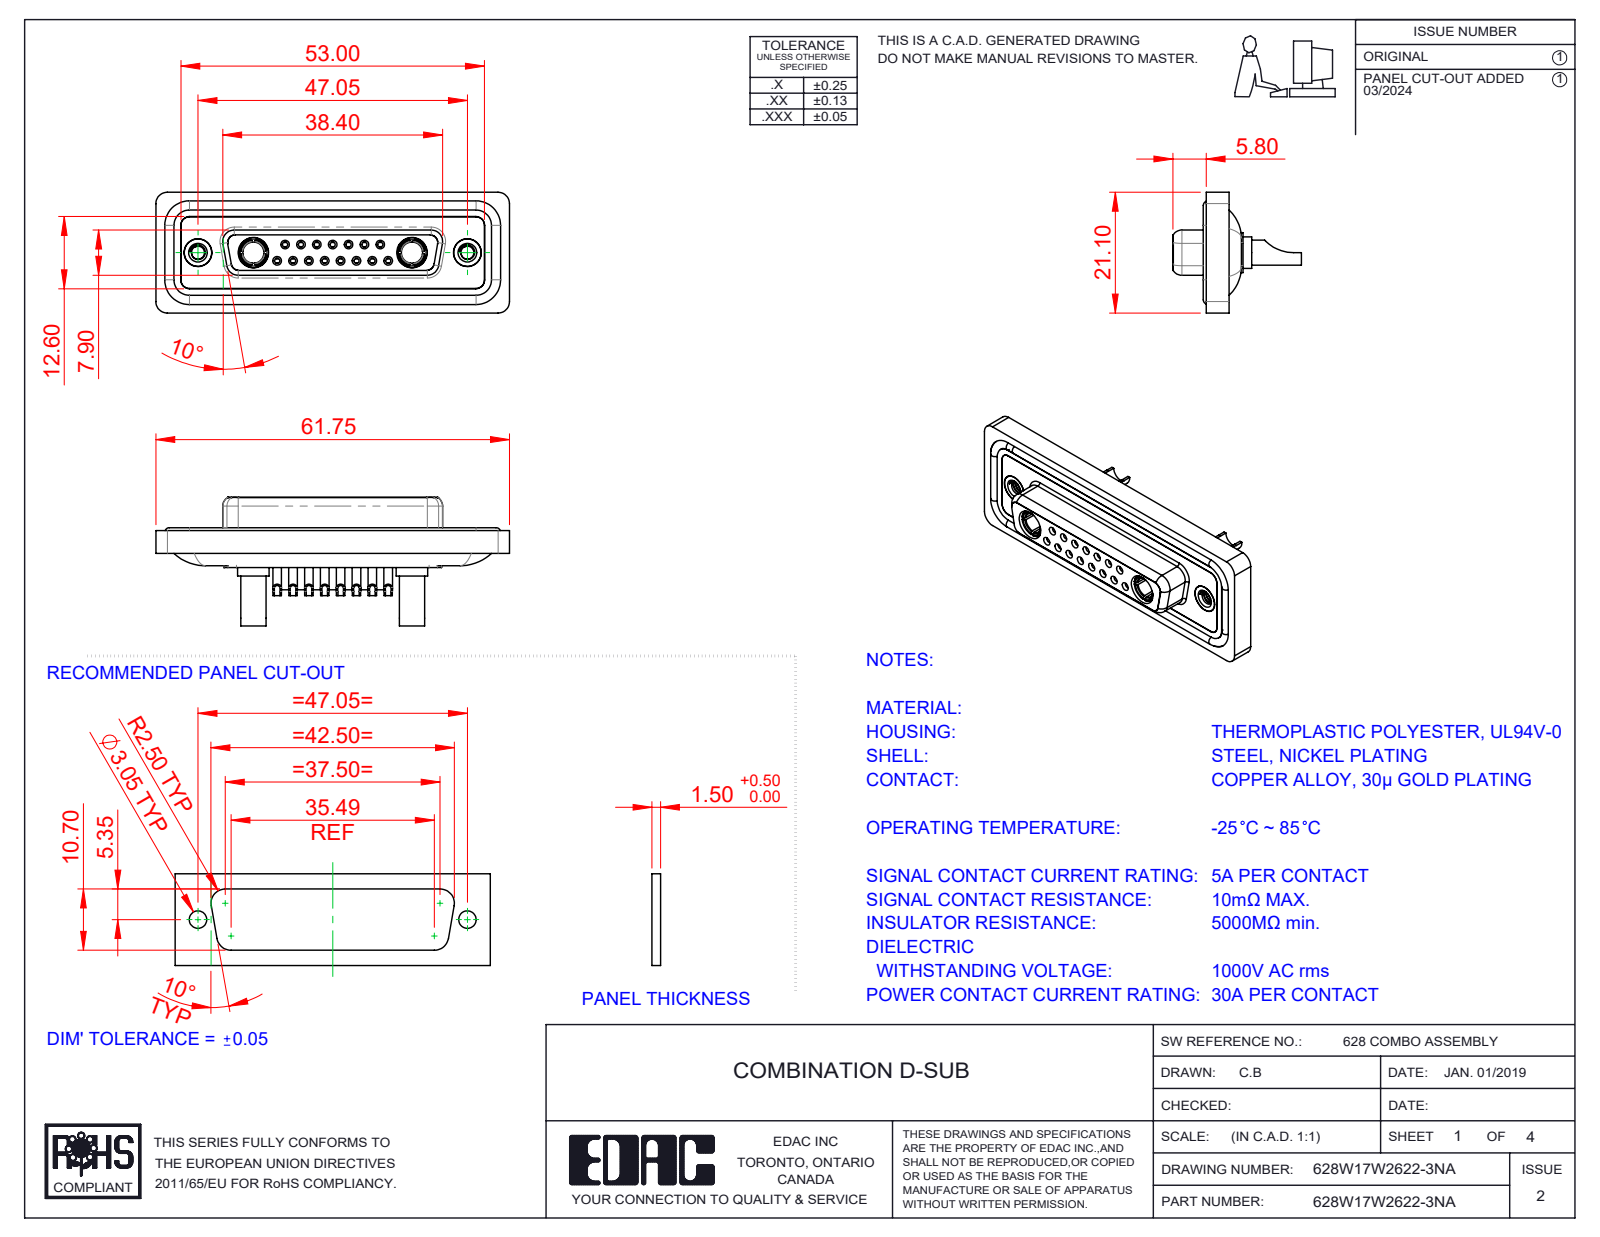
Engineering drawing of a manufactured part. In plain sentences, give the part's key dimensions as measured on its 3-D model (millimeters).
The part is named "628Combo Shell Front_25 Contacts; 628Combo Waterproof Housing_25 Contacts; Power Socket_30A SC; 628Combo Shell Rear_25 Contacts (+5 more)". Its 3-D file was written by "SolidWorks 2023 (CONFIG_CONTROL_DESIGN)". It is 26 solids with 1369 faces: 424 planar, 557 cylindrical and 388 other. Overall it measures 61.75 by 22.45 by 21.1 millimeters. Its volume is 8 405 cubic millimeters and its surface area 14 228 square millimeters. Round holes: 15 of diameter 0.9, 15 of diameter 1, 15 of diameter 1.1, 15 of diameter 1.5, 15 of diameter 2, 8 of diameter 1.6, 7 of diameter 1.7, 4 of diameter 4.85, 2 of diameter 2.26, 2 of diameter 3.5, 2 of diameter 3.7, 2 of diameter 4. Round bosses or shafts: 15 of diameter 2.2, 11 of diameter 1.6, 2 of diameter 5.5, 2 of diameter 5.2, 2 of diameter 4.96, 2 of diameter 4.95, 2 of diameter 4.8, 2 of diameter 4.75. Partial cylindrical surfaces (rounded edges, fillets, slot ends): 22 of radius 1.5, 18 of radius 2, 8 of radius 1.35, 8 of radius 1.6, 6 of radius 1, 4 of radius 0.25, 4 of radius 0.5, 4 of radius 0.6. The main face-to-face distances are 0.4, 1.8, 7.45, 5.65, 6.6, 0.5, 7.05, 1.6, 2.9, 1.1. The hole center spacings are 3.16, 2.77, 8.31, 5.54, 5.03, 5.04, 7.49, 11.08.
